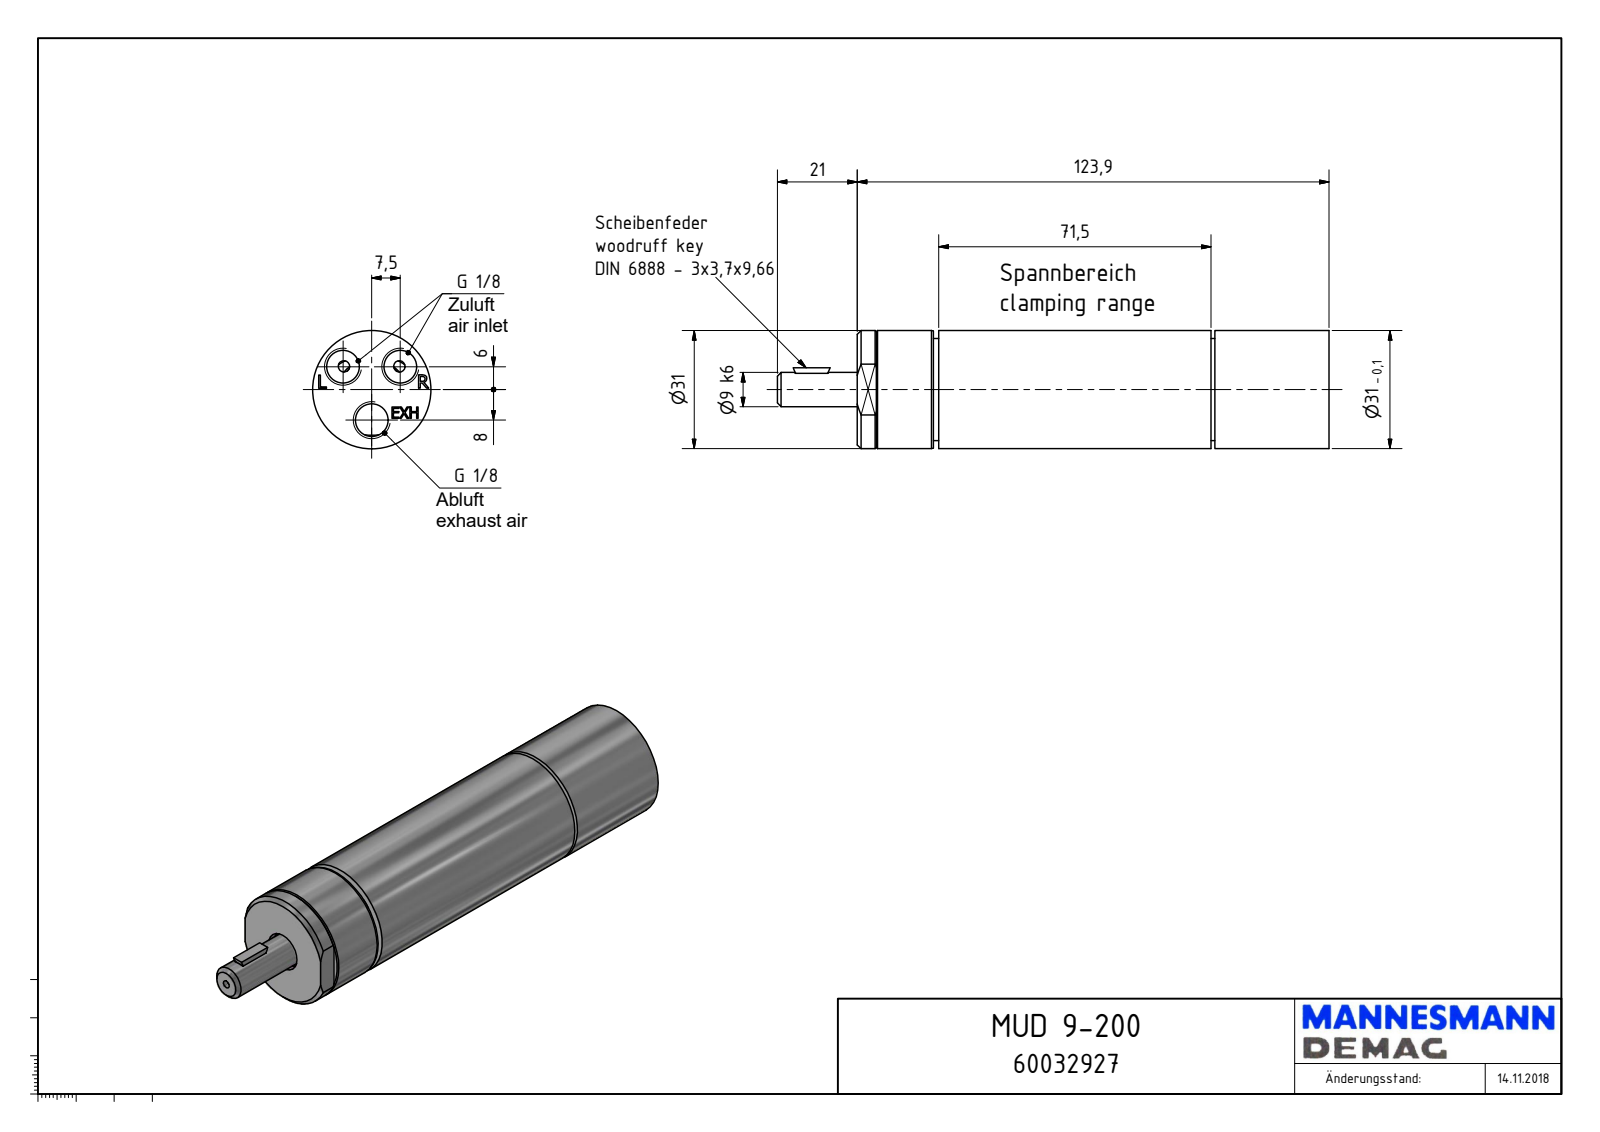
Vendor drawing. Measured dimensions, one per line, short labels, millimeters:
name: MUD 9-200_60032927
written by: Autodesk Inventor 2018 (AUTOMOTIVE_DESIGN)
unit: mm
bodies: 1 solid, 145 faces (90 planar, 23 cylindrical, 32 other)
size: 144.9 × 31 × 31
volume: 92 495 mm³; area: 16 563 mm²
holes: 3× ⌀8.57, 1× ⌀1, 1× ⌀10.36, 1× ⌀10.5, 1× ⌀16, 1× ⌀29.3
bosses: 1× ⌀31, 1× ⌀28, 1× ⌀26.79, 1× ⌀9
rounds: 1× R5, 1× R5.25
face distances: 123.9, 21.4, 102.5, 92.9, 71.5, 31, 115.45, 94.05, 22.55, 8.45
hole spacings: 9.6, 15.88, 8, 15
